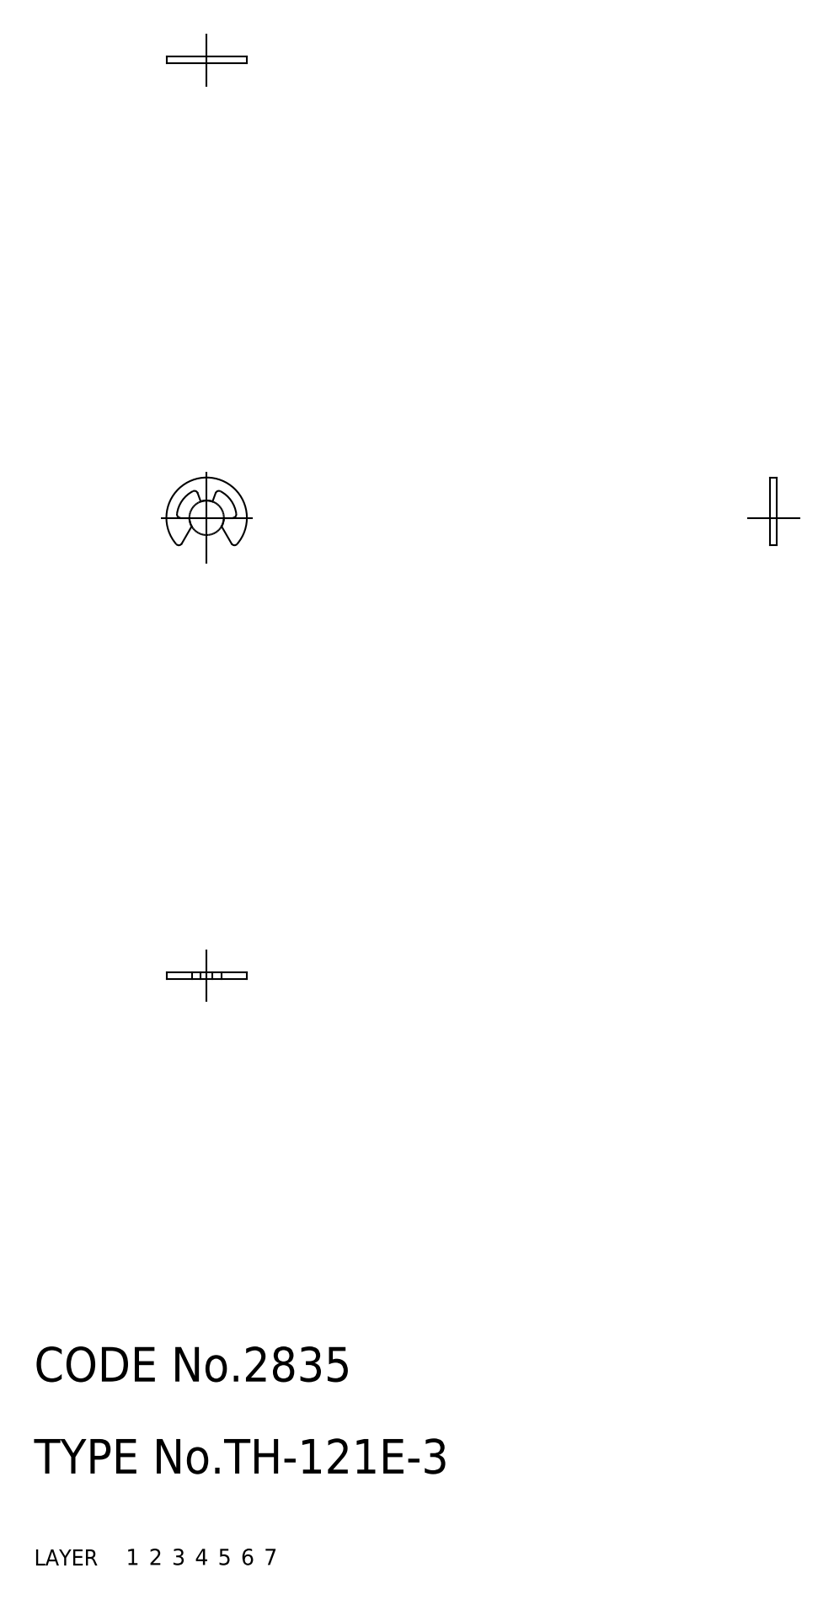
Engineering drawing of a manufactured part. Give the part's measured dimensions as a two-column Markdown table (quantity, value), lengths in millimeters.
| quantity | value |
| --- | --- |
| part name | retainer |
| STEP written by | CADfix (AUTOMOTIVE_DESIGN) |
| units | millimeters |
| bodies | 1 solid, 20 faces (0 planar, 0 cylindrical, 20 other) |
| overall size | 7 × 5.89 × 0.6 |
| volume | 11 mm³ |
| surface area | 55 mm² |
